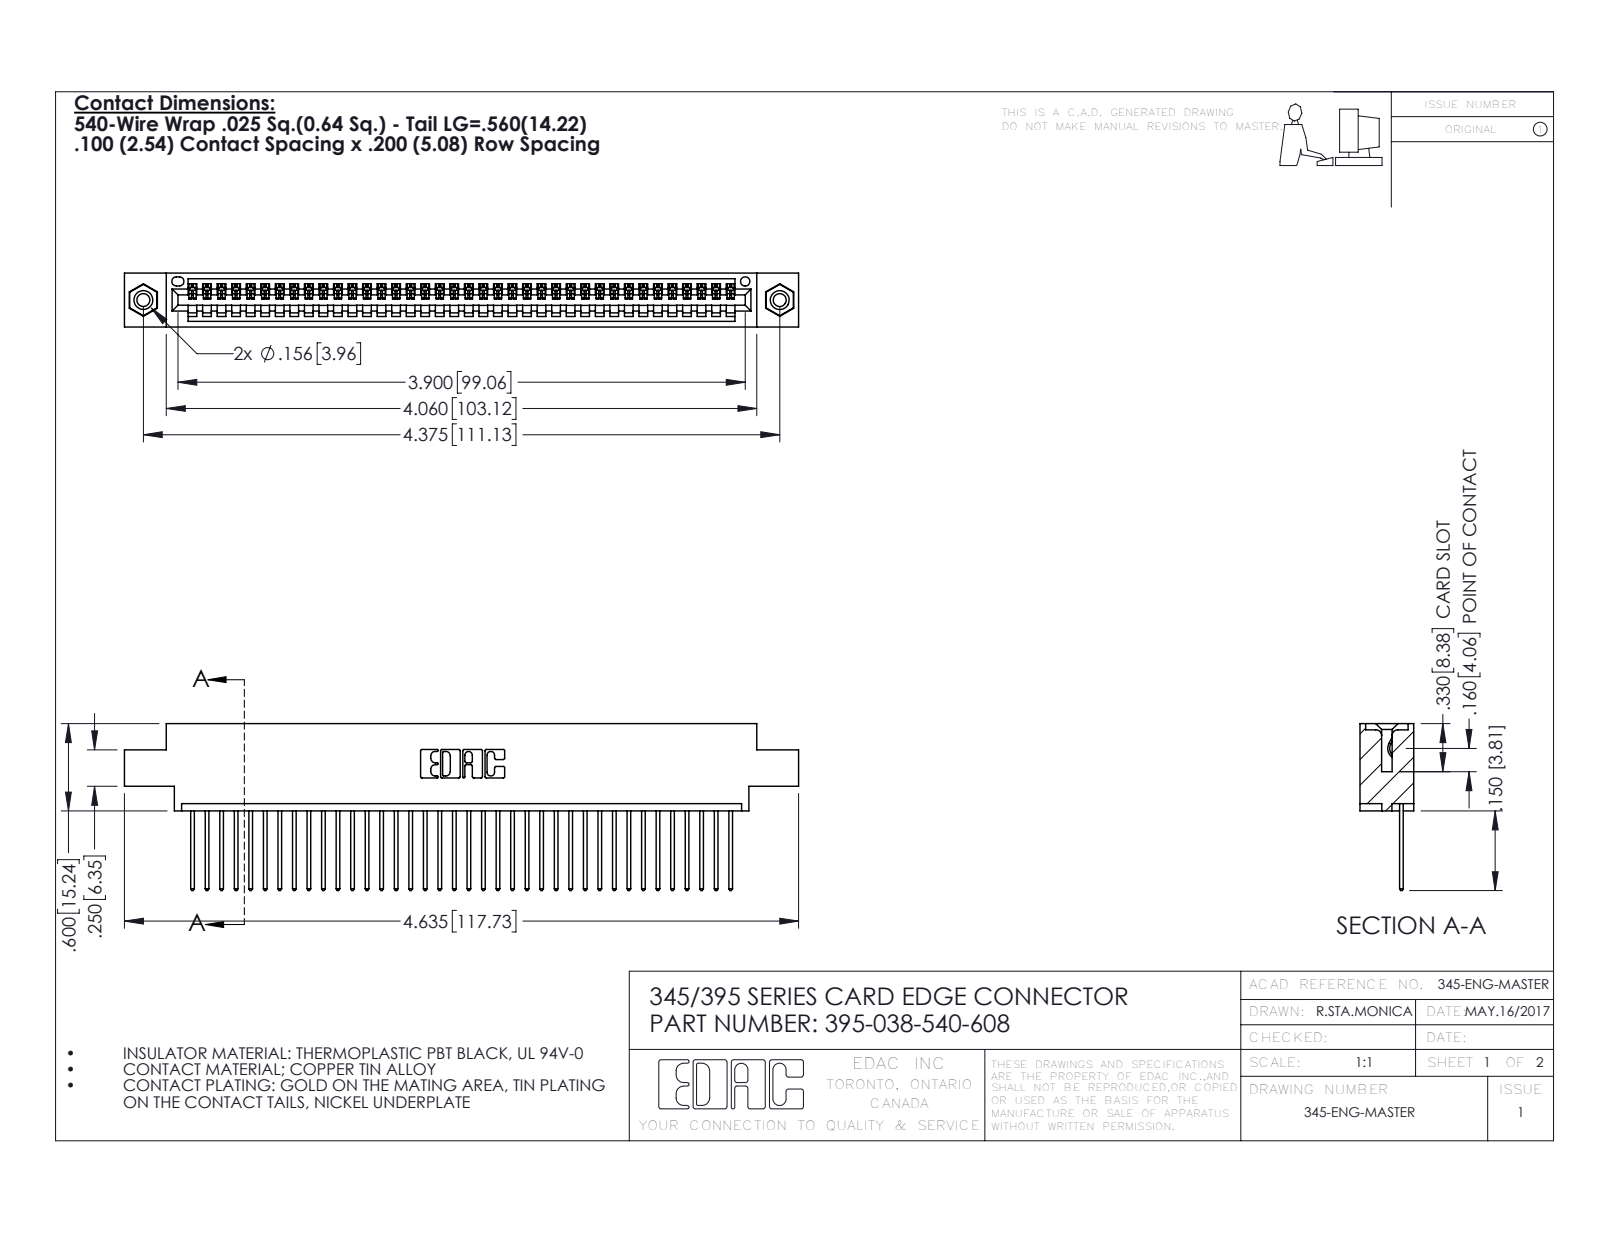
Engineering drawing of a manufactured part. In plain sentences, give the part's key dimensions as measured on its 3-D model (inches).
The part is named "395-038-540-608; 345-250-001_345-250-003-102; 345-292-001_345-293-140; 345 Part_0.170 Offset - 0.156 Dia-TI". Its 3-D file was written by "SolidWorks 2016 (CONFIG_CONTROL_DESIGN)". It is 41 solids with 2394 faces: 1636 planar, 742 cylindrical and 16 other. Overall it measures 4.635 by 1.147 by 0.37 inches. Its volume is 0.676 cubic inches and its surface area 23.54 square inches. Round holes: 2 of diameter 0.089, 2 of diameter 0.125, 2 of diameter 0.156, 1 of diameter 0.064. Round bosses or shafts: 2 of diameter 0.155. Partial cylindrical surfaces (rounded edges, fillets, slot ends): 76 of radius 0.006, 76 of radius 0.01, 22 of radius 0.01, 6 of radius 0.007, 6 of radius 0.031, 3 of radius 0.026, 2 of radius 0.031, 2 of radius 0.04. The main face-to-face distances are 0.072, 0.298, 0.37, 0.098, 0.272, 0.025, 0.2, 0.225, 0.175, 0.149. The hole center spacings are 0.27, 4.139, 4.375.
